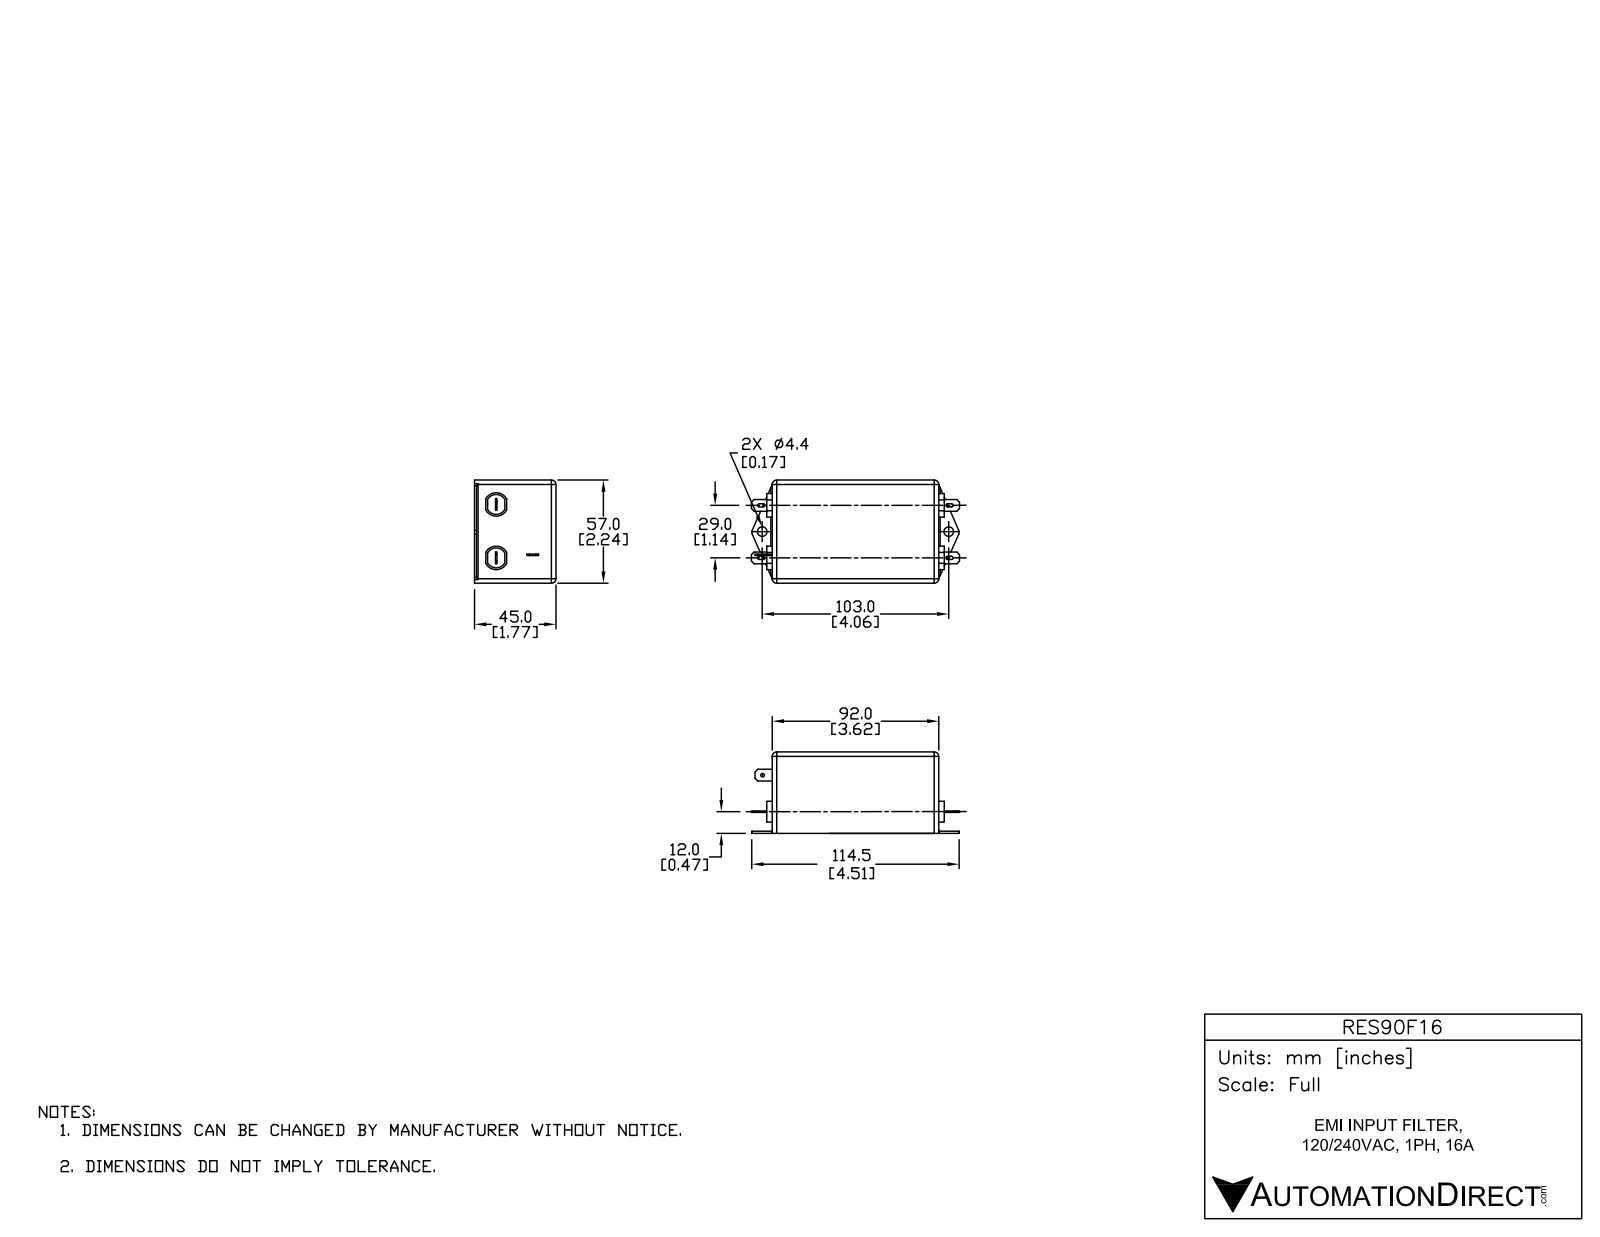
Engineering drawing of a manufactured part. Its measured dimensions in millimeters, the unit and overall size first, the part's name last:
Units: millimetres
Overall size (bounding box): 115 × 57 × 45
Round holes (diameter × count): ⌀5.3 ×2, ⌀2 ×1
Partial cylindrical surfaces — rounded edges, fillets, slot ends (radius × count): R2.5 ×10, R0.88 ×8, R0.75 ×2, R5.5 ×2, R6.5 ×2
Main face-to-face distances: 45, 57, 92, 1.5, 1.2, 43.8, 93.5, 95, 0.8, 11.6
Hole centre spacings: 103
Volume: 237 234 mm³ · Surface area: 25 864 mm²
Bodies: 1 solid, 133 faces (79 planar, 50 cylindrical, 4 other)
Part name (STEP PRODUCT): RES90F16
STEP written by: SolidWorks 2015 (AUTOMOTIVE_DESIGN)
